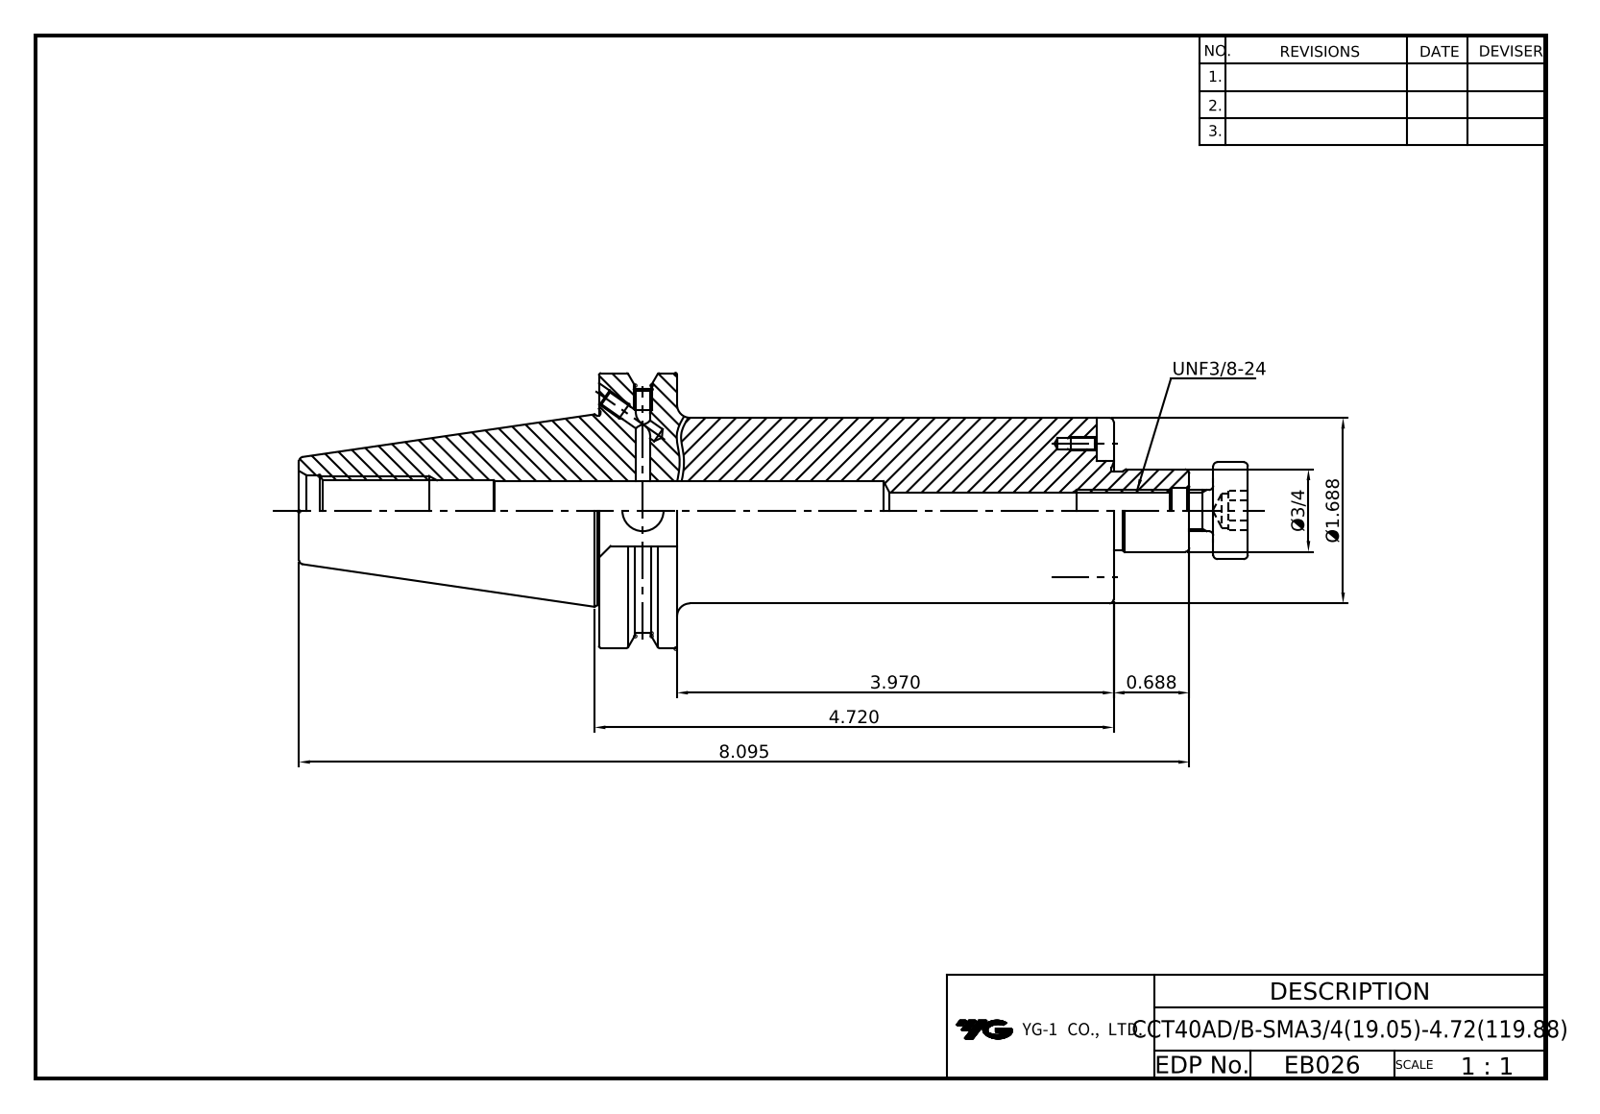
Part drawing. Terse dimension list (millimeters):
name: LO-CCT40ADB-SMA19.05-119.888; DRIVE KEY-7.93x7.93x9.5; HEX'' WRENCH BOLT-UNC#5-40x5_16L; COLLAR BOLT-UNF3_8-24x24L
written by: Autodesk Inventor 2022 (AUTOMOTIVE_DESIGN)
unit: mm
bodies: 6 solids, 179 faces (90 planar, 47 cylindrical, 42 other)
size: 218.6 × 63.5 × 61.1
volume: 249 100 mm³; area: 42 970 mm²
holes: 4× ⌀3.3, 2× ⌀2.5, 2× ⌀3.3, 2× ⌀4, 2× ⌀4.2, 2× ⌀5.4, 1× ⌀8, 1× ⌀8.4, 1× ⌀9.5, 1× ⌀10.5, 1× ⌀13, 1× ⌀13.4
bosses: 2× ⌀5.2, 2× ⌀3.2, 1× ⌀63.5, 1× ⌀43.8, 1× ⌀42.9, 1× ⌀22.4, 1× ⌀19.1, 1× ⌀18.5
rounds: 2× R4, 1× R28.1
face distances: 18.1, 118.9, 100.8, 149.4, 131.3, 30.5, 114.9, 96.9, 4, 34.4
hole spacings: 15.5, 30.9
